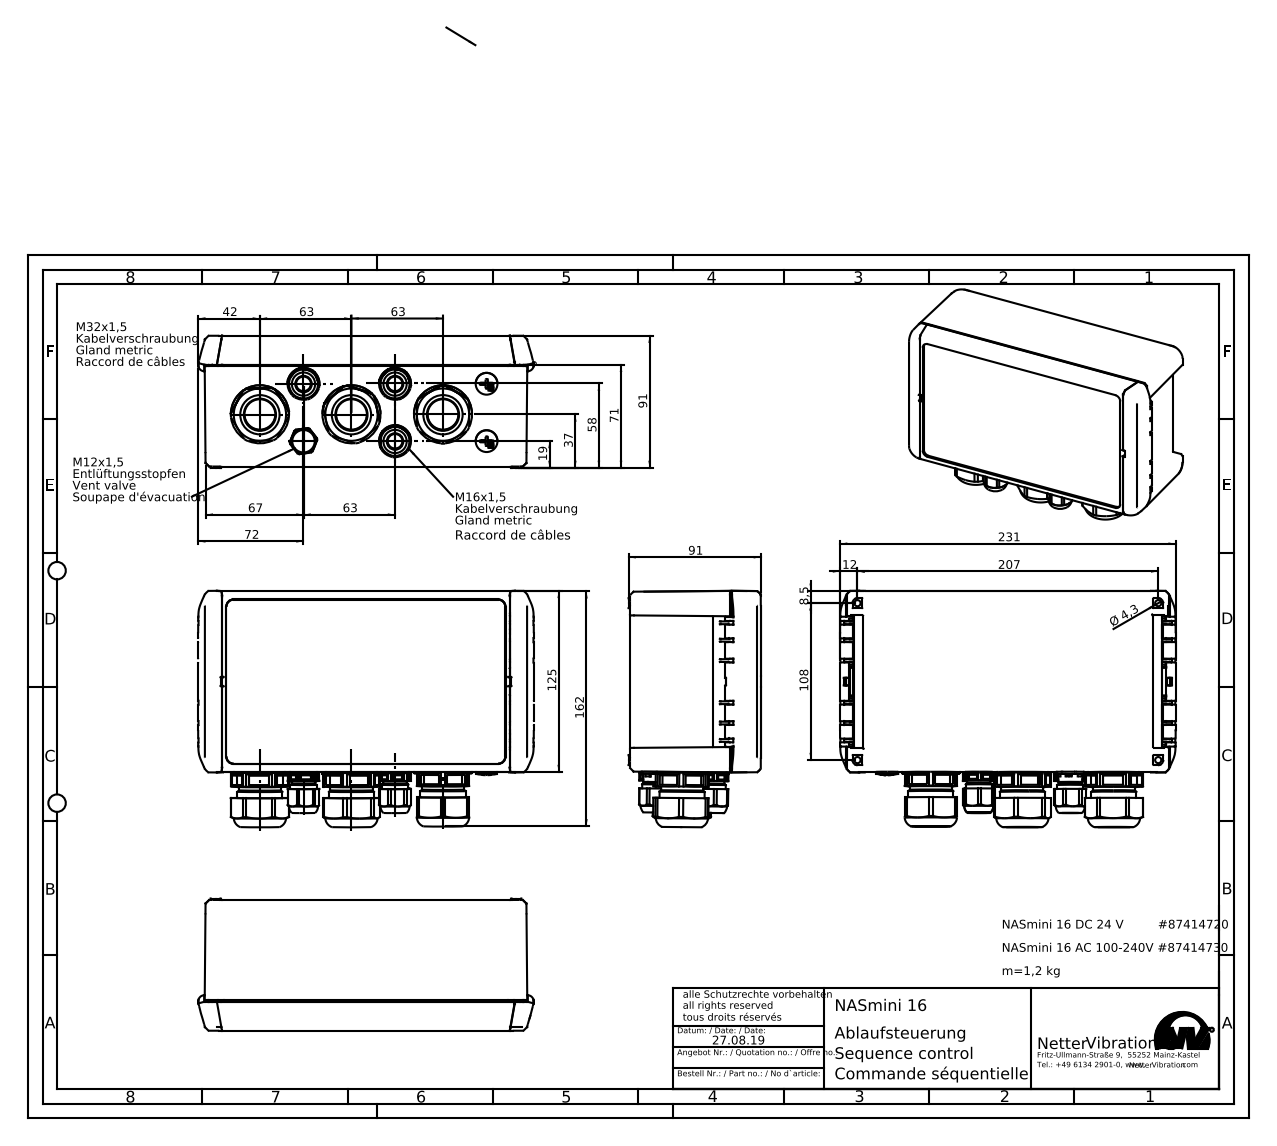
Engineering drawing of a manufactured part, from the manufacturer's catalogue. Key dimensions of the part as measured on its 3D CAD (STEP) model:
Part name (STEP PRODUCT): NAS mini 16 #87414720+#87414730
STEP written by: SolidWorks 2015 (AUTOMOTIVE_DESIGN)
Units: millimetres
Bodies: 34 solids, 4075 faces (1297 planar, 1551 cylindrical, 1227 other)
Overall size (bounding box): 231 × 162.73 × 91.1
Volume: 498 449 mm³ · Surface area: 381 878 mm²
Round holes (diameter × count): ⌀3.5 ×28, ⌀3 ×27, ⌀1 ×10, ⌀4.2 ×10, ⌀13 ×6, ⌀3.24 ×5, ⌀4.5 ×5, ⌀6 ×5, ⌀4.25 ×4, ⌀10.3 ×3, ⌀17 ×3, ⌀21.3 ×3
Round bosses / shafts (diameter × count): ⌀4 ×7, ⌀16 ×5, ⌀10 ×5, ⌀8 ×5, ⌀5.74 ×5, ⌀4.4 ×5, ⌀2.9 ×4, ⌀40 ×3
Partial cylindrical surfaces — rounded edges, fillets, slot ends (radius × count): R0.5 ×327, R0.3 ×216, R2 ×75, R1 ×30, R2.25 ×16, R15 ×16, R0.2 ×8, R5 ×8
Main face-to-face distances: 3, 85.1, 88.1, 88.3, 85.3, 82.1, 3.2, 3.01, 81.16, 3.94
Hole centre spacings: 63, 1.06, 39.5, 126, 95.34, 35.25, 1.72, 16
